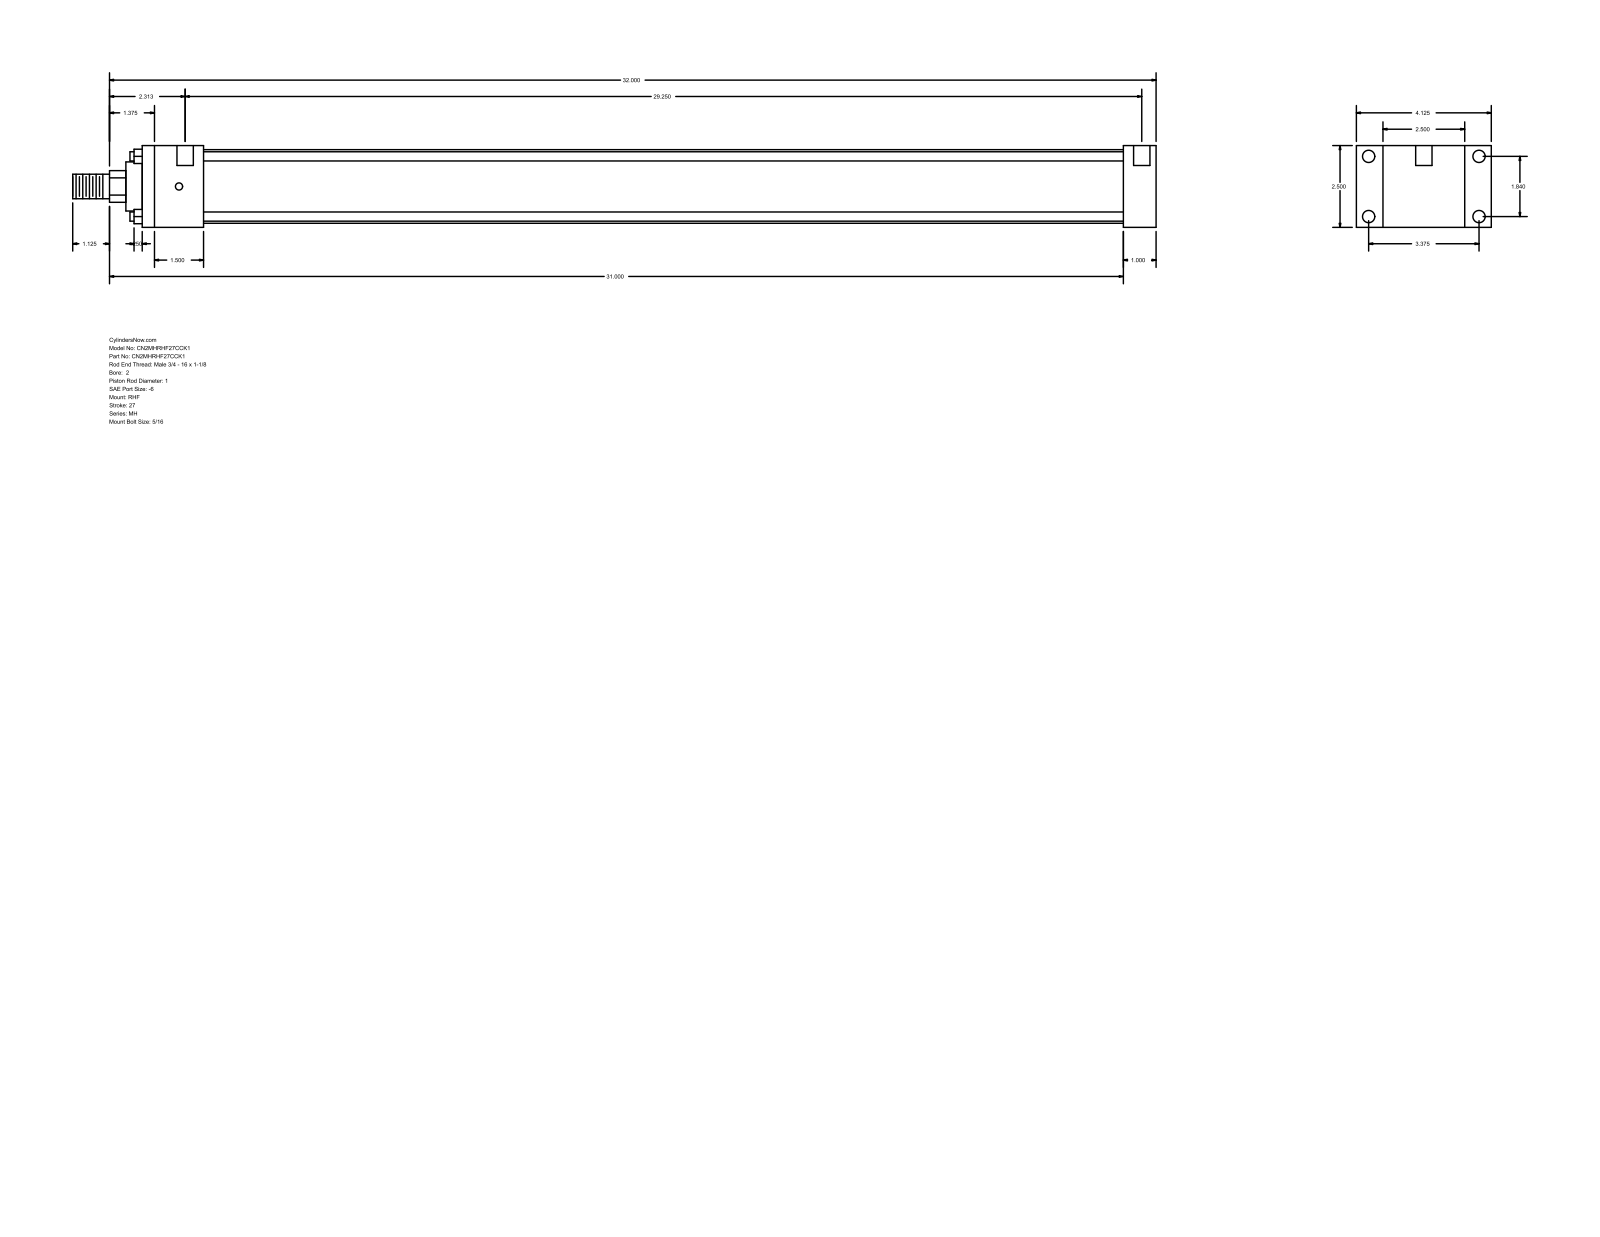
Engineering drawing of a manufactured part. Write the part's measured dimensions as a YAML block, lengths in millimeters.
part_name: "MH_RHF__0200_1"
step_written_by: "GSSL Pune (CONFIG_CONTROL_DESIGN)"
units: millimeters
bodies: {solids: 0, faces: 88, planar: 60, cylindrical: 28, other: 0}
overall_size: [841.38, 104.78, 63.5]
round_holes:
  - {diameter: 5.56, count: 4}
  - {diameter: 9.53, count: 4}
  - {diameter: 12.7, count: 2}
round_bosses_or_shafts:
  - {diameter: 7.14, count: 4}
  - {diameter: 57.15, count: 1}
  - {diameter: 38.1, count: 1}
  - {diameter: 25.4, count: 1}
  - {diameter: 19.05, count: 1}
partial_cylinders:
  - {radius: 12.29, count: 1}
face_to_face_distances: [63.5, 25.4, 20.64, 84.14, 787.4, 762, 104.78, 47.63, 714.37, 739.77]
hole_center_spacings: [46.74, 85.72, 97.63, 750.88, 3.17, 4.76, 742.95, 746.12]
